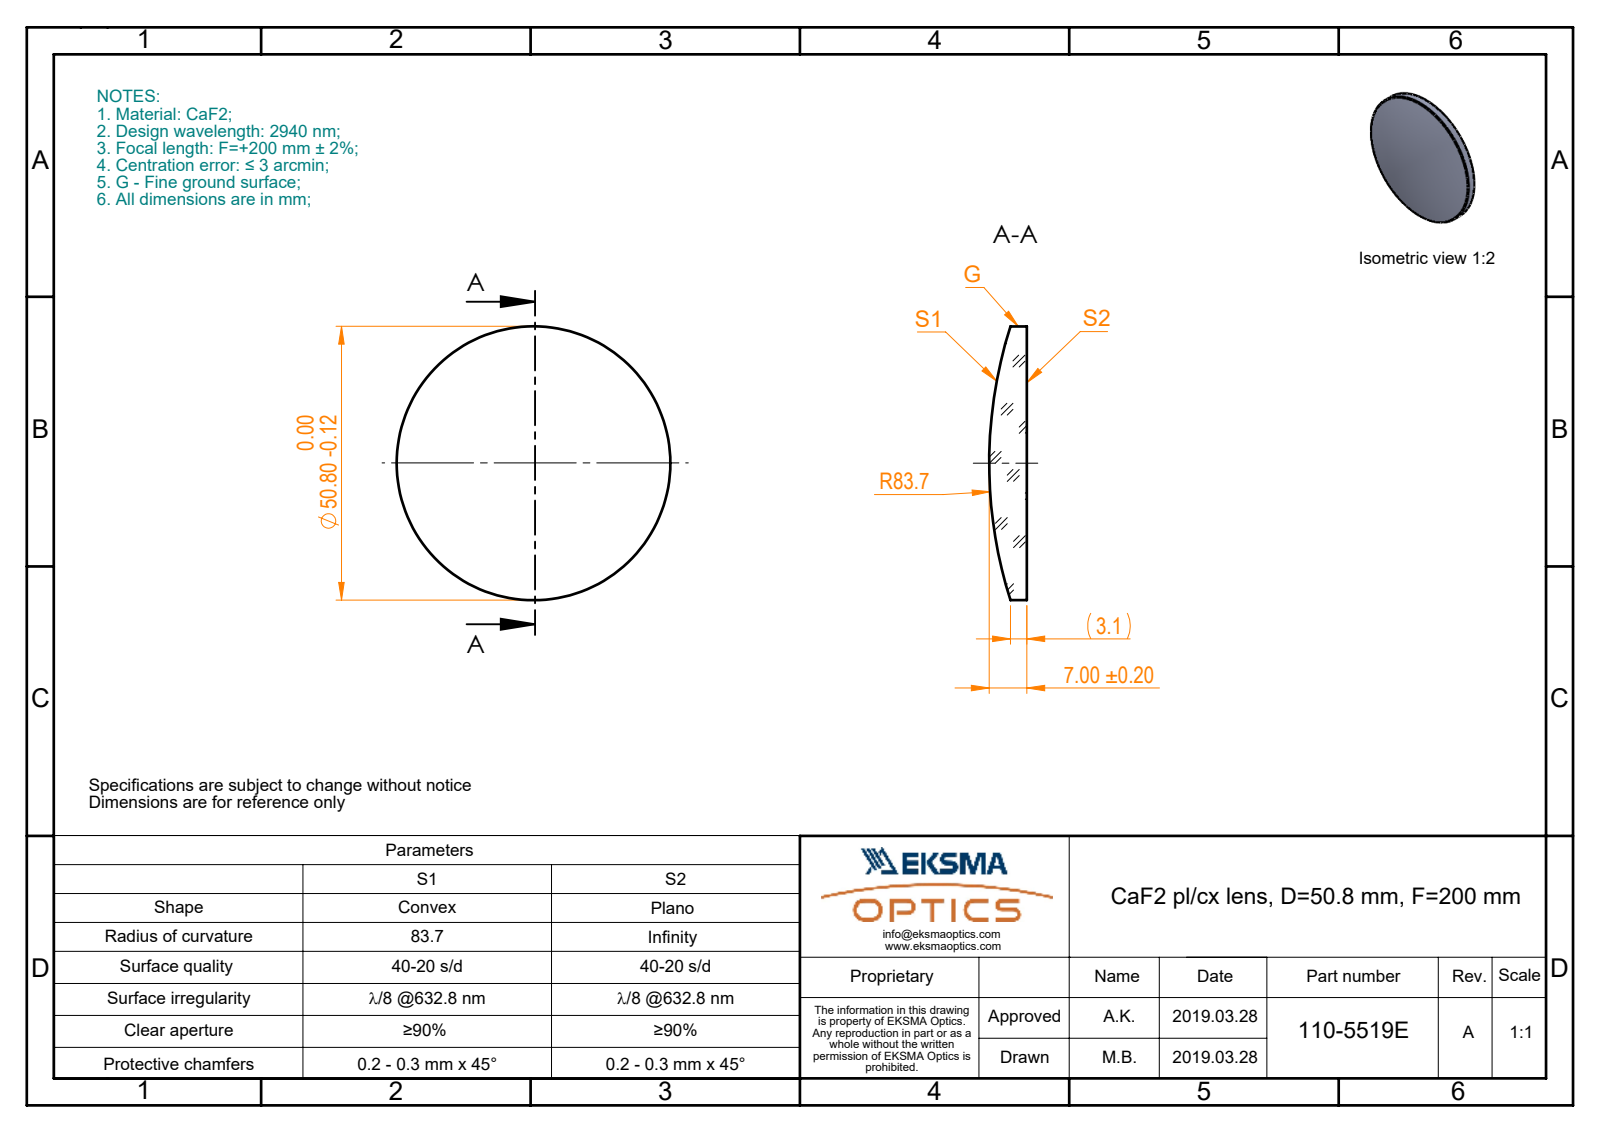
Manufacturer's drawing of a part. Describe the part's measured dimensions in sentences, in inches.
The part is named "110-5519E CaF2 pl-cx 50.8 F200". Its 3-D file was written by "SolidWorks 2017 (CONFIG_CONTROL_DESIGN)". It is 1 solid with 5 faces: 1 planar, 2 cylindrical and 2 other. Overall it measures 2 by 2 by 0.276 inches. Its volume is 0.624 cubic inches and its surface area 7.115 square inches. Round bosses or shafts: 1 of diameter 2.
